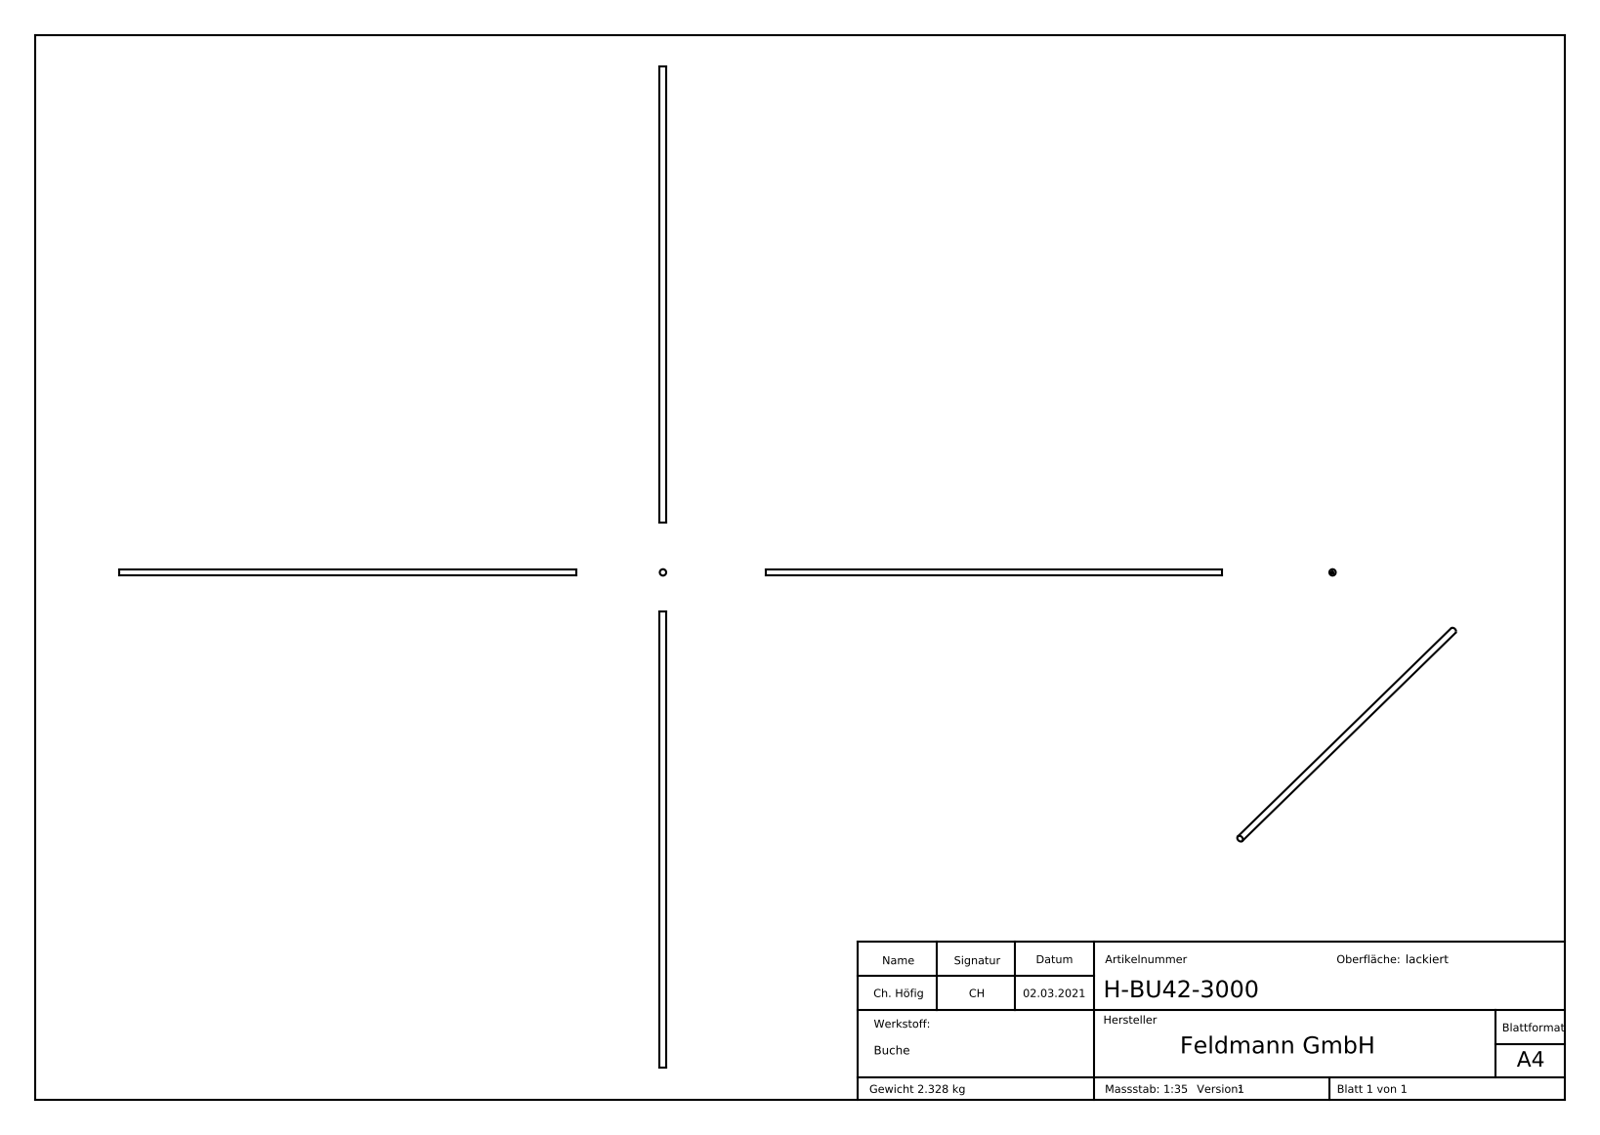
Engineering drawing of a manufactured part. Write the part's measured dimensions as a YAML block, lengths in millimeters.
part_name: "H-BU42-3000"
step_written_by: "SolidWorks 2018 (CONFIG_CONTROL_DESIGN)"
units: millimeters
bodies: {solids: 1, faces: 295, planar: 162, cylindrical: 2, other: 131}
overall_size: [3000, 42, 42]
volume: 4156000
surface_area: 398625
round_bosses_or_shafts:
  - {diameter: 42, count: 1}
face_to_face_distances: [3000, 2999.9, 3.07, 2.23, 3.2, 1.49, 4.61, 1.12, 3.78, 0.34]
